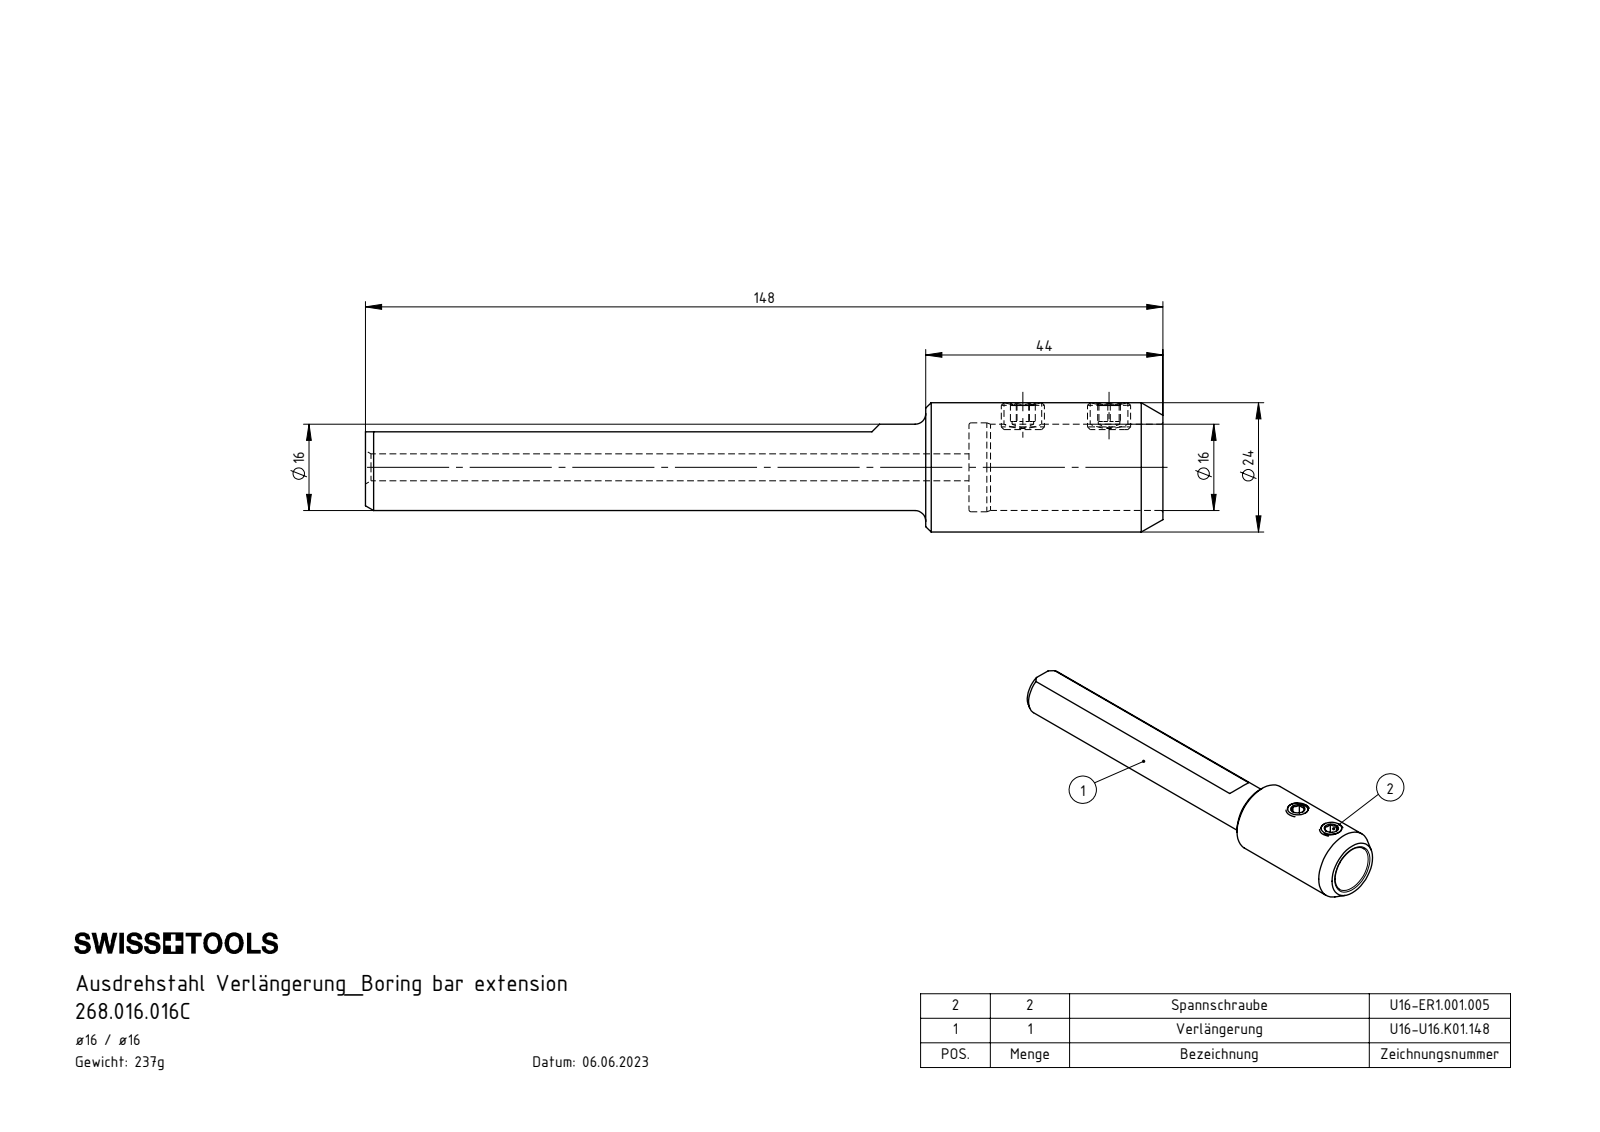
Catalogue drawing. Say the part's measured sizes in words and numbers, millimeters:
The part is named "U16-U16.K01.148_A; U16-ER1.001.005_A; 268.016.016C". Its 3-D file was written by "SolidWorks 2022 (AUTOMOTIVE_DESIGN)". It is 3 solids with 89 faces: 34 planar, 22 cylindrical and 33 other. Overall it measures 148 by 24 by 24 millimeters. Its volume is 30 231 cubic millimeters and its surface area 13 212 square millimeters. Round holes: 2 of diameter 4, 2 of diameter 7, 1 of diameter 5, 1 of diameter 16, 1 of diameter 16.5. Round bosses or shafts: 2 of diameter 8, 1 of diameter 24. The main face-to-face distances are 112, 0.4, 148, 36, 104, 8, 44, 5.4, 5, 4. The hole center spacings are 16.
